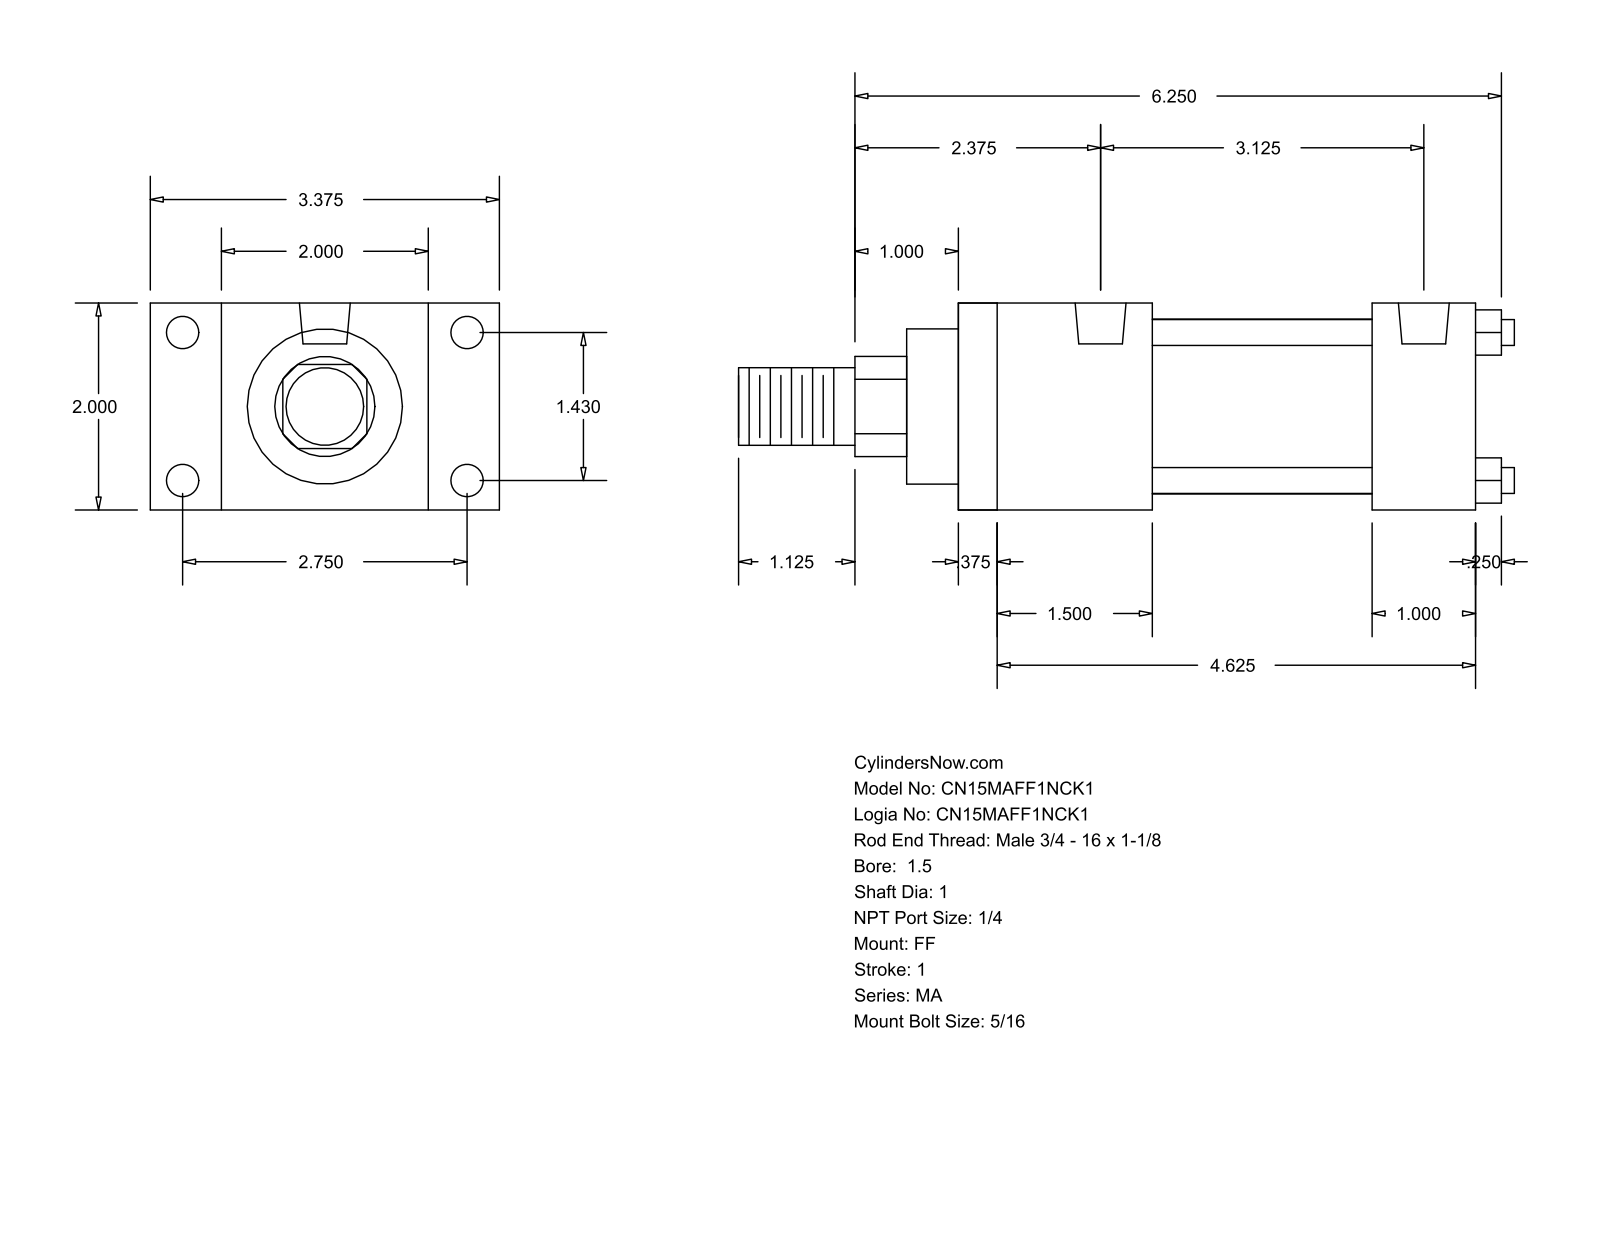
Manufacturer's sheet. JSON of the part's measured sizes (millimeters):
{"part_name": "MA_FF__0150_1", "step_written_by": "GSSL Pune (CONFIG_CONTROL_DESIGN)", "units": "millimeters", "bodies": {"solids": 0, "faces": 92, "planar": 64, "cylindrical": 28, "other": 0}, "overall_size": [190.5, 85.72, 50.8], "round_holes": [[7.94, 8], [12.49, 2]], "round_bosses_or_shafts": [[6.35, 4], [42.93, 1], [38.1, 1], [25.4, 1], [19.05, 1]], "partial_cylinders_radius": [[12.29, 1]], "face_to_face_distances": [50.8, 127, 9.52, 117.48, 53.97, 101.6, 25.4, 47.63, 38.11, 92.08], "hole_center_spacings": [36.32, 69.84, 78.72, 79.37]}
